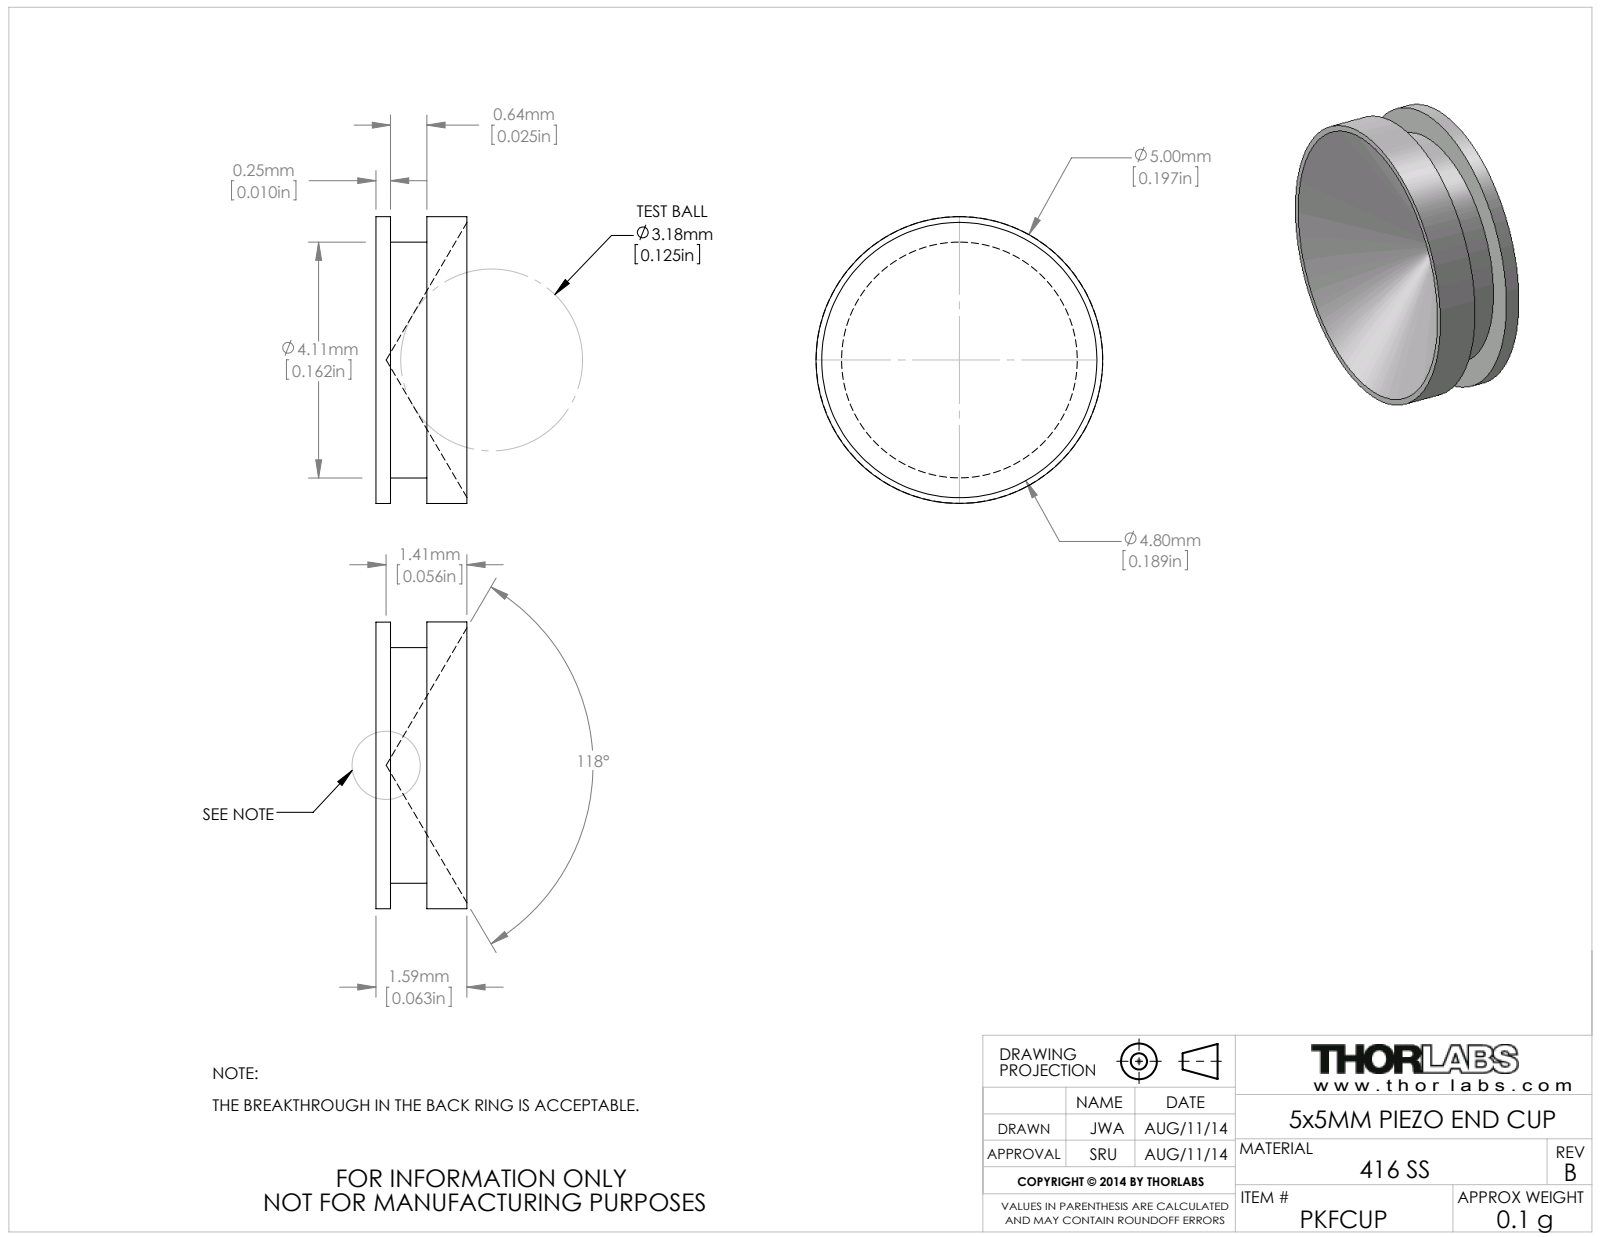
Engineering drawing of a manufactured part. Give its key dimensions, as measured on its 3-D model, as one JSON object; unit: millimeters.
{"part_name": "PKFCUP", "step_written_by": "SolidWorks 2012 (AUTOMOTIVE_DESIGN)", "units": "millimeters", "bodies": {"solids": 1, "faces": 12, "planar": 4, "cylindrical": 6, "other": 2}, "overall_size": [5, 5, 1.59], "volume_mm3": 19, "surface_area_mm2": 78, "round_bosses_or_shafts": [[5, 1], [4.11, 1]], "face_to_face_distances": [0.89, 0.64, 1.59, 1.34, 0.7]}
